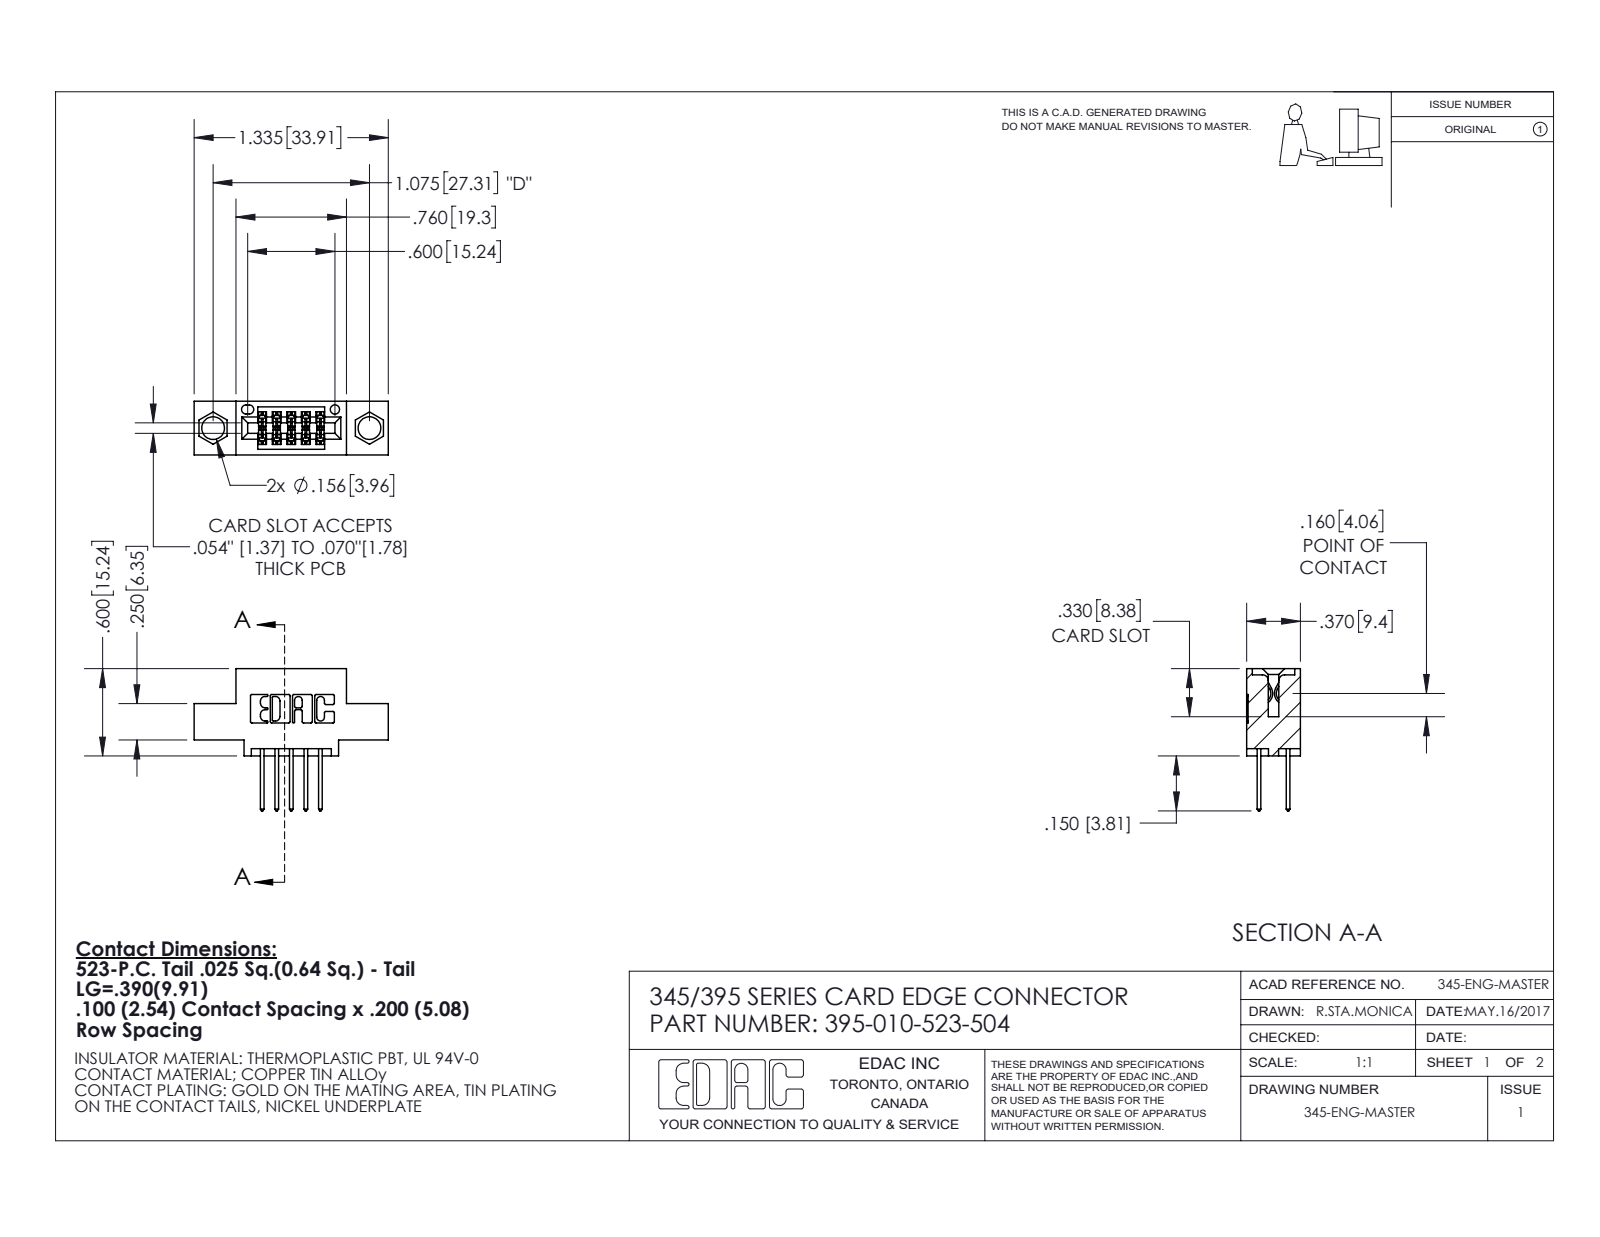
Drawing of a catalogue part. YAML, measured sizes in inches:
part_name: "395-010-523-504; 345-292-001_345-293-123; 345 Part_0.110 Offset - 0.156 Dia-TI"
step_written_by: "SolidWorks 2020 (CONFIG_CONTROL_DESIGN)"
units: inches
bodies: {solids: 11, faces: 644, planar: 428, cylindrical: 216, other: 0}
overall_size: [1.335, 0.977, 0.37]
volume: 0.17
surface_area: 5.342
round_holes:
  - {diameter: 0.156, count: 2}
  - {diameter: 0.064, count: 1}
partial_cylinders:
  - {radius: 0.01, count: 22}
  - {radius: 0.006, count: 15}
  - {radius: 0.01, count: 10}
  - {radius: 0.007, count: 6}
  - {radius: 0.031, count: 6}
  - {radius: 0.026, count: 3}
  - {radius: 0.014, count: 2}
  - {radius: 0.019, count: 2}
face_to_face_distances: [0.2, 0.298, 0.072, 0.37, 0.1, 0.098, 0.272, 0.025, 0.225, 0.25]
hole_center_spacings: [0.27, 0.847, 1.075]
